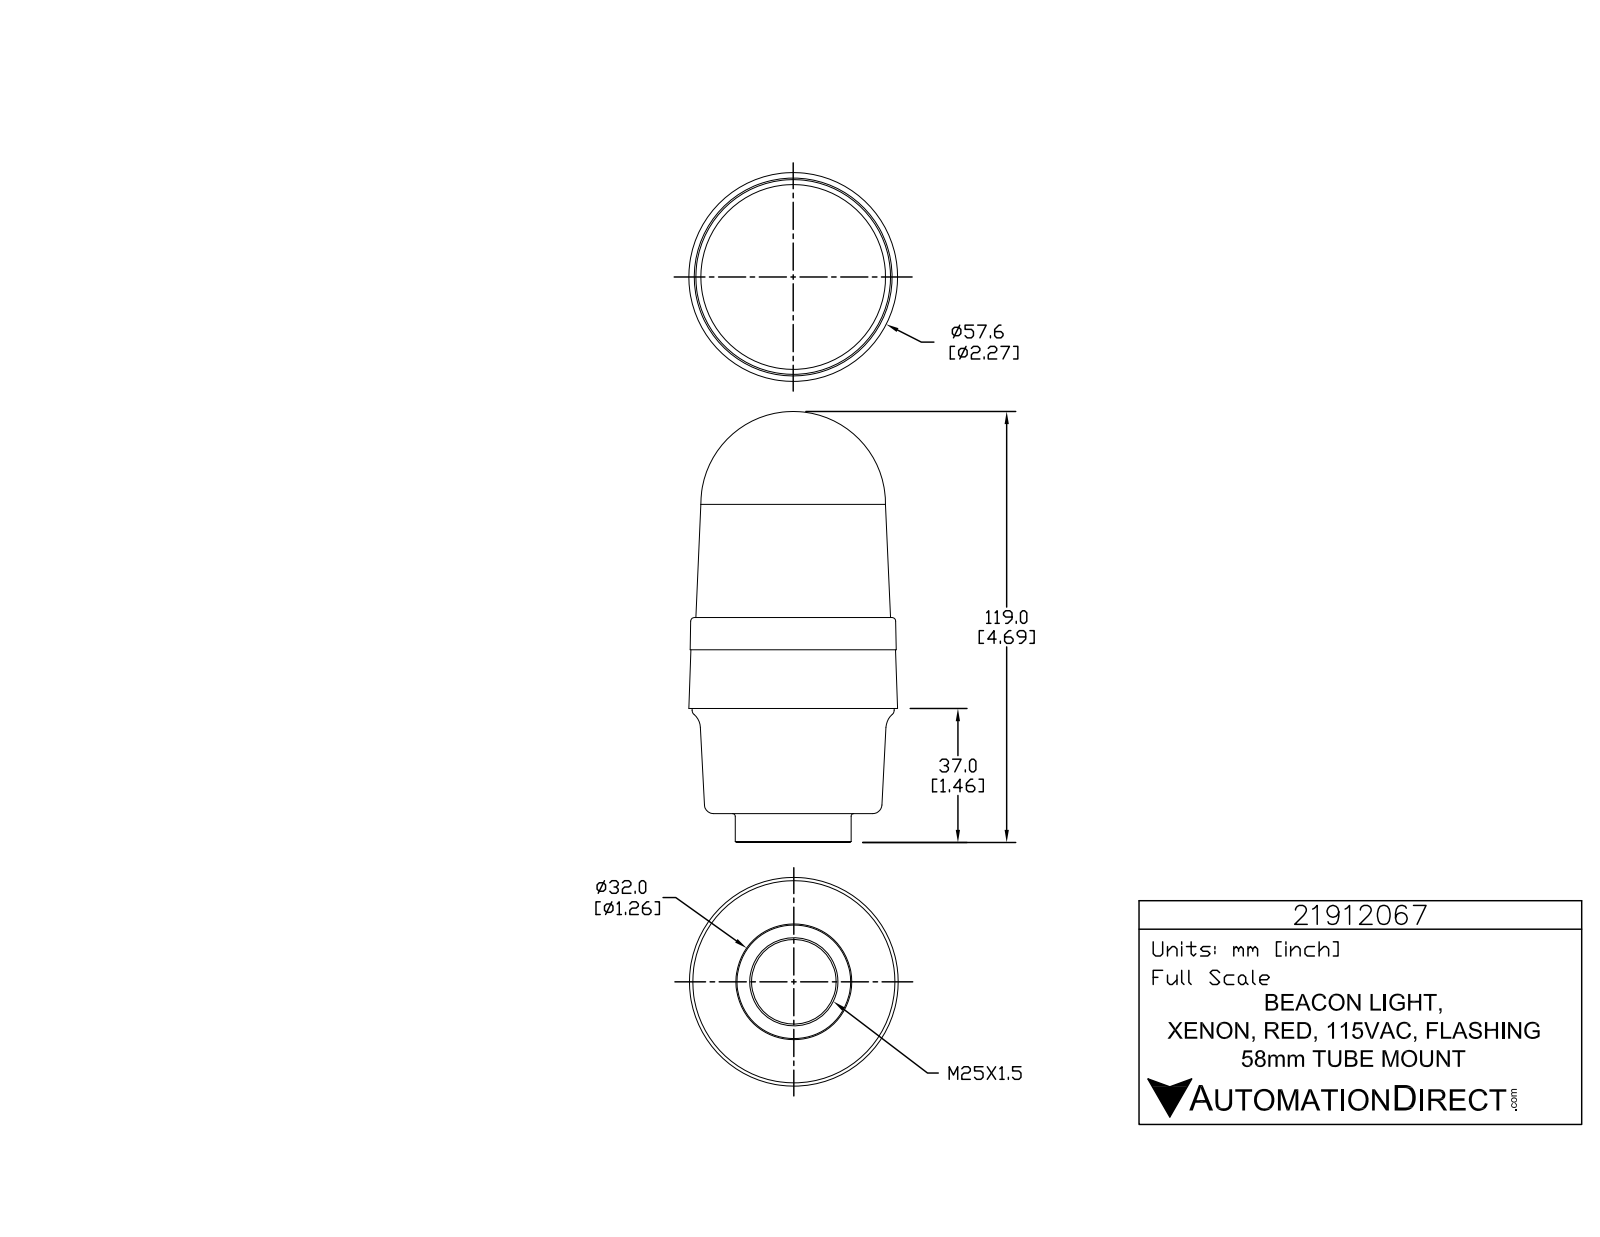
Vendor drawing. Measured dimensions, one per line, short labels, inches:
name: 21912067
written by: SolidWorks 2015 (AUTOMOTIVE_DESIGN)
unit: in
bodies: 1 solid, 791 faces (525 planar, 168 cylindrical, 98 other)
size: 4.685 × 2.269 × 2.269
volume: 13.89 in³; area: 34.06 in²
holes: 3× ⌀0.039, 1× ⌀0.92
bosses: 3× ⌀0.226, 3× ⌀0.056, 1× ⌀2.197, 1× ⌀1.26
rounds: 6× R0.008, 6× R0.008, 6× R0.008, 6× R0.131, 3× R0.004, 3× R0.005, 3× R0.008, 3× R0.008
face distances: 0.315, 1.142, 1.457, 0.988, 2.13, 2.445, 0.35, 0.638, 1.78, 2.094
